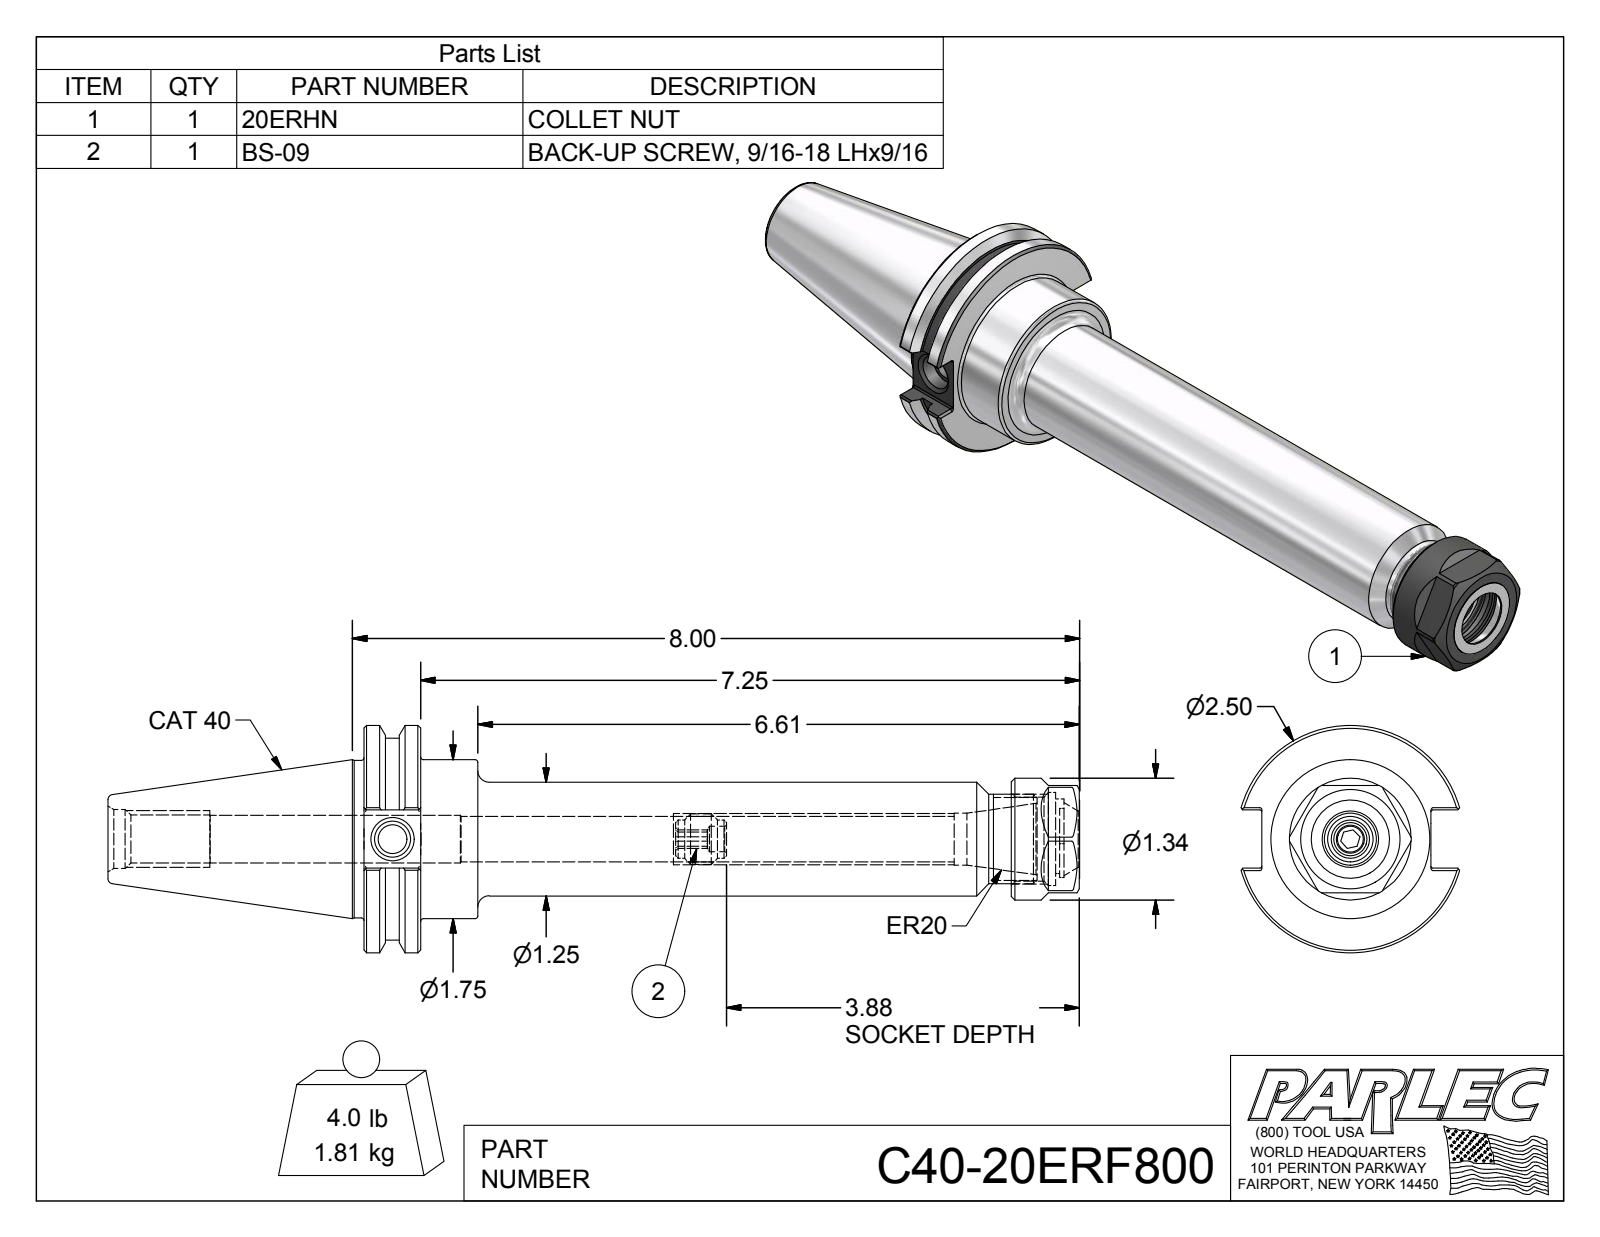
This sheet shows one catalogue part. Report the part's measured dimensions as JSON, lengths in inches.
{"part_name": "C40-20ERF800; C40-20ER8-1; 20ERHN; BS-09", "step_written_by": "Autodesk Inventor 2012 (AUTOMOTIVE_DESIGN)", "units": "inches", "bodies": {"solids": 3, "faces": 147, "planar": 65, "cylindrical": 40, "other": 42}, "overall_size": [10.688, 2.5, 2.403], "volume_in3": 14.02, "surface_area_in2": 77.35, "round_holes": [[0.281, 1], [0.315, 1], [0.399, 1], [0.502, 1], [0.526, 1], [0.527, 1], [0.57, 1], [0.62, 1], [0.648, 1], [0.82, 1], [0.925, 1], [1.024, 1]], "round_bosses_or_shafts": [[2.5, 1], [2.219, 1], [1.75, 1], [1.73, 1], [1.339, 1], [1.25, 1], [0.984, 1], [0.86, 1]], "partial_cylinders_radius": [[0.02, 12], [0.423, 1]], "face_to_face_distances": [0.625, 1.181, 1.255, 0.63, 7.122, 6.497, 5.867, 0.27, 0.911, 7.87], "hole_center_spacings": [0.037]}
